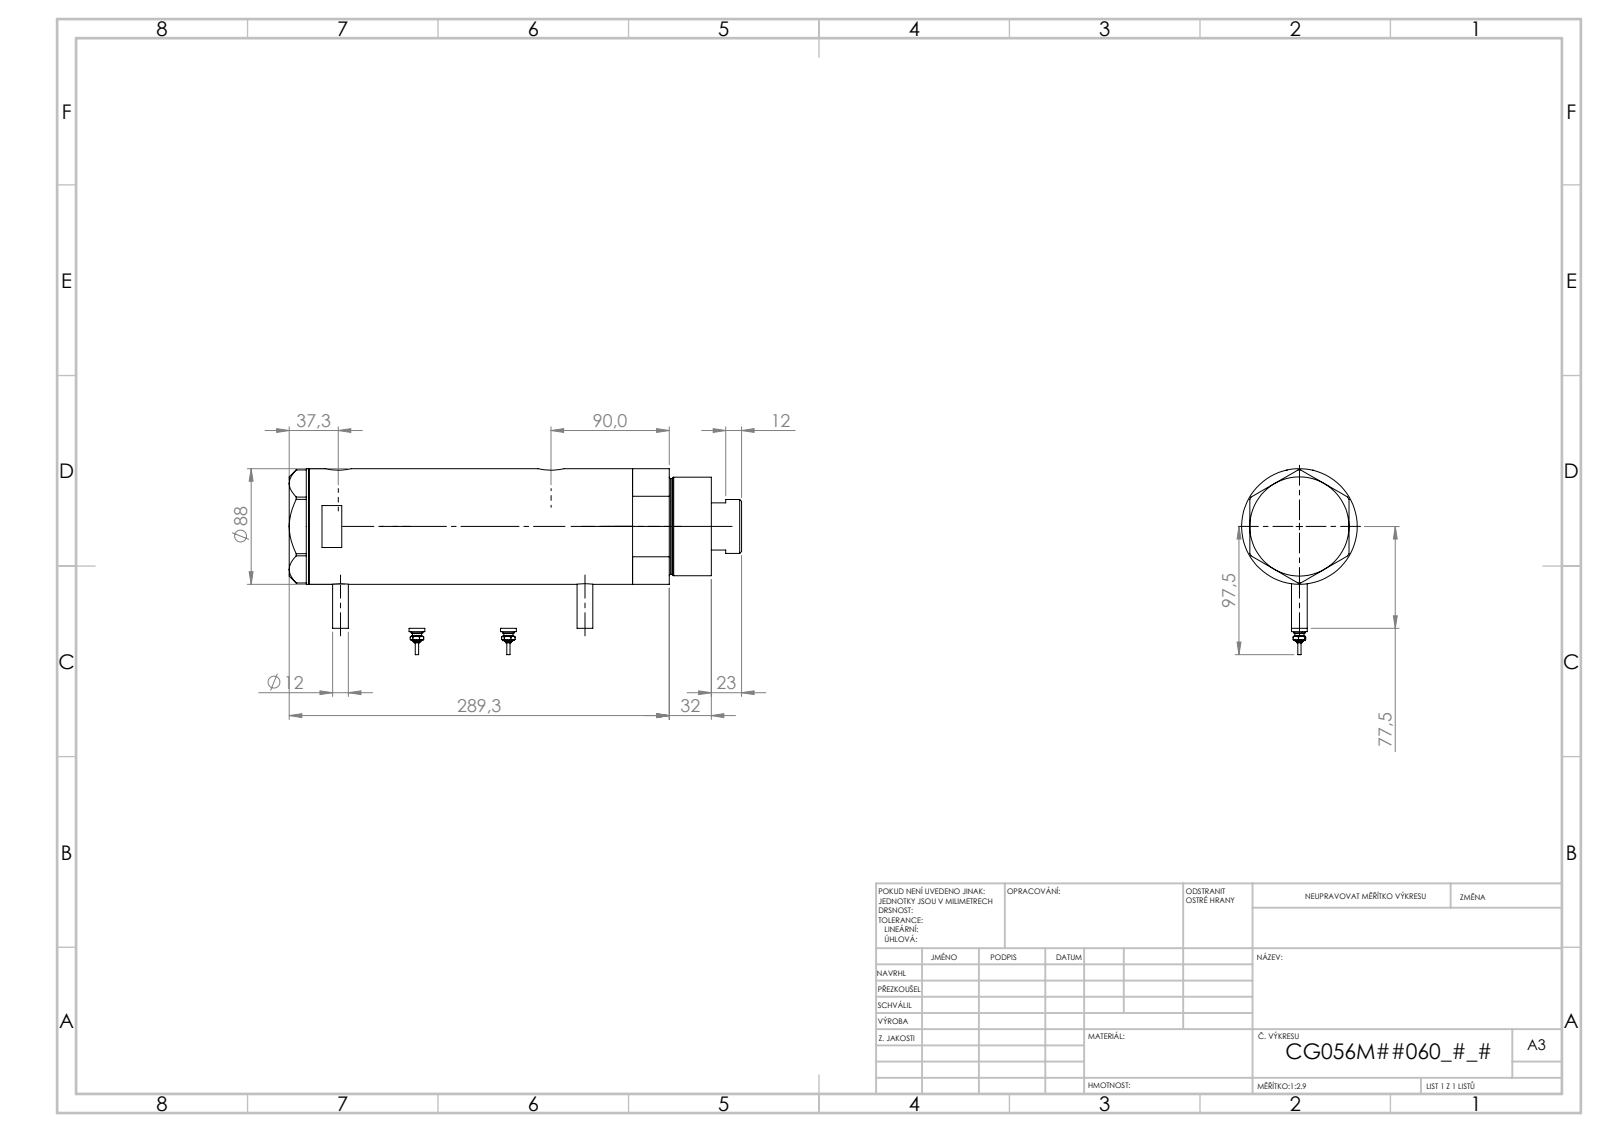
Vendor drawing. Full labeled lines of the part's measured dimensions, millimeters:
Part name (STEP PRODUCT): V270CG_MIDDLE; V270CG_SWITCH; V270CG_FRONT; V270CG_BACK (+1 more)
STEP written by: SolidWorks 2019 (CONFIG_CONTROL_DESIGN)
Units: millimetres
Bodies: 6 solids, 232 faces (81 planar, 77 cylindrical, 74 other)
Overall size (bounding box): 284.47 × 120.3 × 88
Volume: 1 465 000 mm³ · Surface area: 217 267 mm²
Round holes (diameter × count): ⌀5 ×2, ⌀12.5 ×2, ⌀13.16 ×2, ⌀20 ×2, ⌀14.5 ×1, ⌀42 ×1, ⌀43.5 ×1, ⌀56 ×1, ⌀60 ×1, ⌀80 ×1
Round bosses / shafts (diameter × count): ⌀12 ×2, ⌀9 ×2, ⌀7 ×2, ⌀4.34 ×2, ⌀2.4 ×2, ⌀88 ×1, ⌀75 ×1, ⌀73 ×1
Main face-to-face distances: 134.4, 26, 108.4, 15, 41, 149.4, 246.47, 261.47, 220.47, 112.07
Hole centre spacings: 1.7, 25.8, 110.3, 112, 136.1, 137.8
